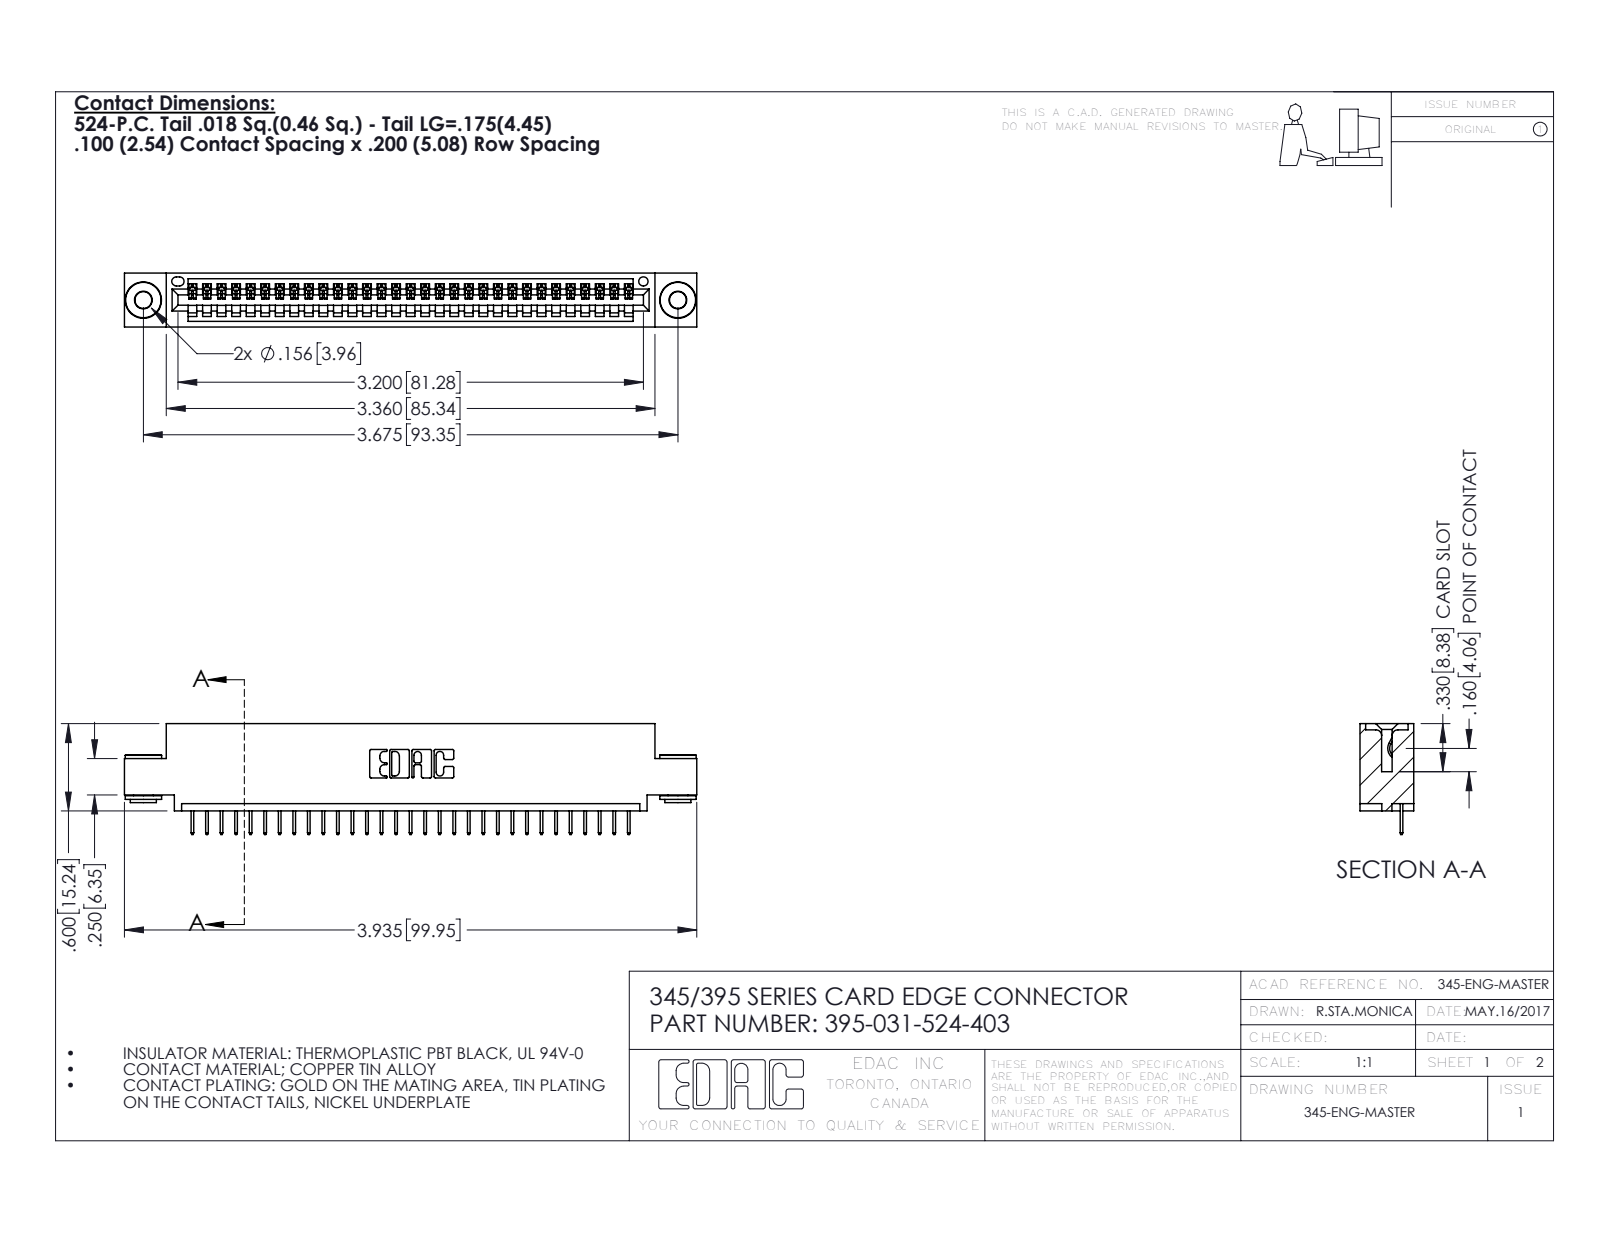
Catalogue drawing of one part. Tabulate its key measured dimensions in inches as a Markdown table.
| quantity | value |
| --- | --- |
| part name | 395-031-524-403; 345-250-002_345-250-002-102; 345-292-001_345-293-124; 345 Part_0.110 Offset - 0.156 Dia-TH |
| STEP written by | SolidWorks 2016 (CONFIG_CONTROL_DESIGN) |
| units | inches |
| bodies | 34 solids, 2090 faces (1520 planar, 562 cylindrical, 8 other) |
| overall size | 3.935 × 0.762 × 0.37 |
| volume | 0.563 in³ |
| surface area | 18.63 in² |
| round holes (diameter × count) | 0.116 × 2, 0.156 × 2, 0.064 × 1 |
| round bosses / shafts (diameter × count) | 0.25 × 2, 0.18 × 2, 0.136 × 2 |
| partial cylindrical surfaces (radius × count) | 0.006 × 62, 0.01 × 22, 0.007 × 6, 0.031 × 6, 0.026 × 3, 0.031 × 2, 0.04 × 2, 0.014 × 1 |
| main face-to-face distances | 0.072, 0.298, 0.37, 0.2, 0.025, 0.098, 0.272, 0.225, 0.072, 0.149 |
| hole center spacings | 0.27, 3.44, 3.675 |
